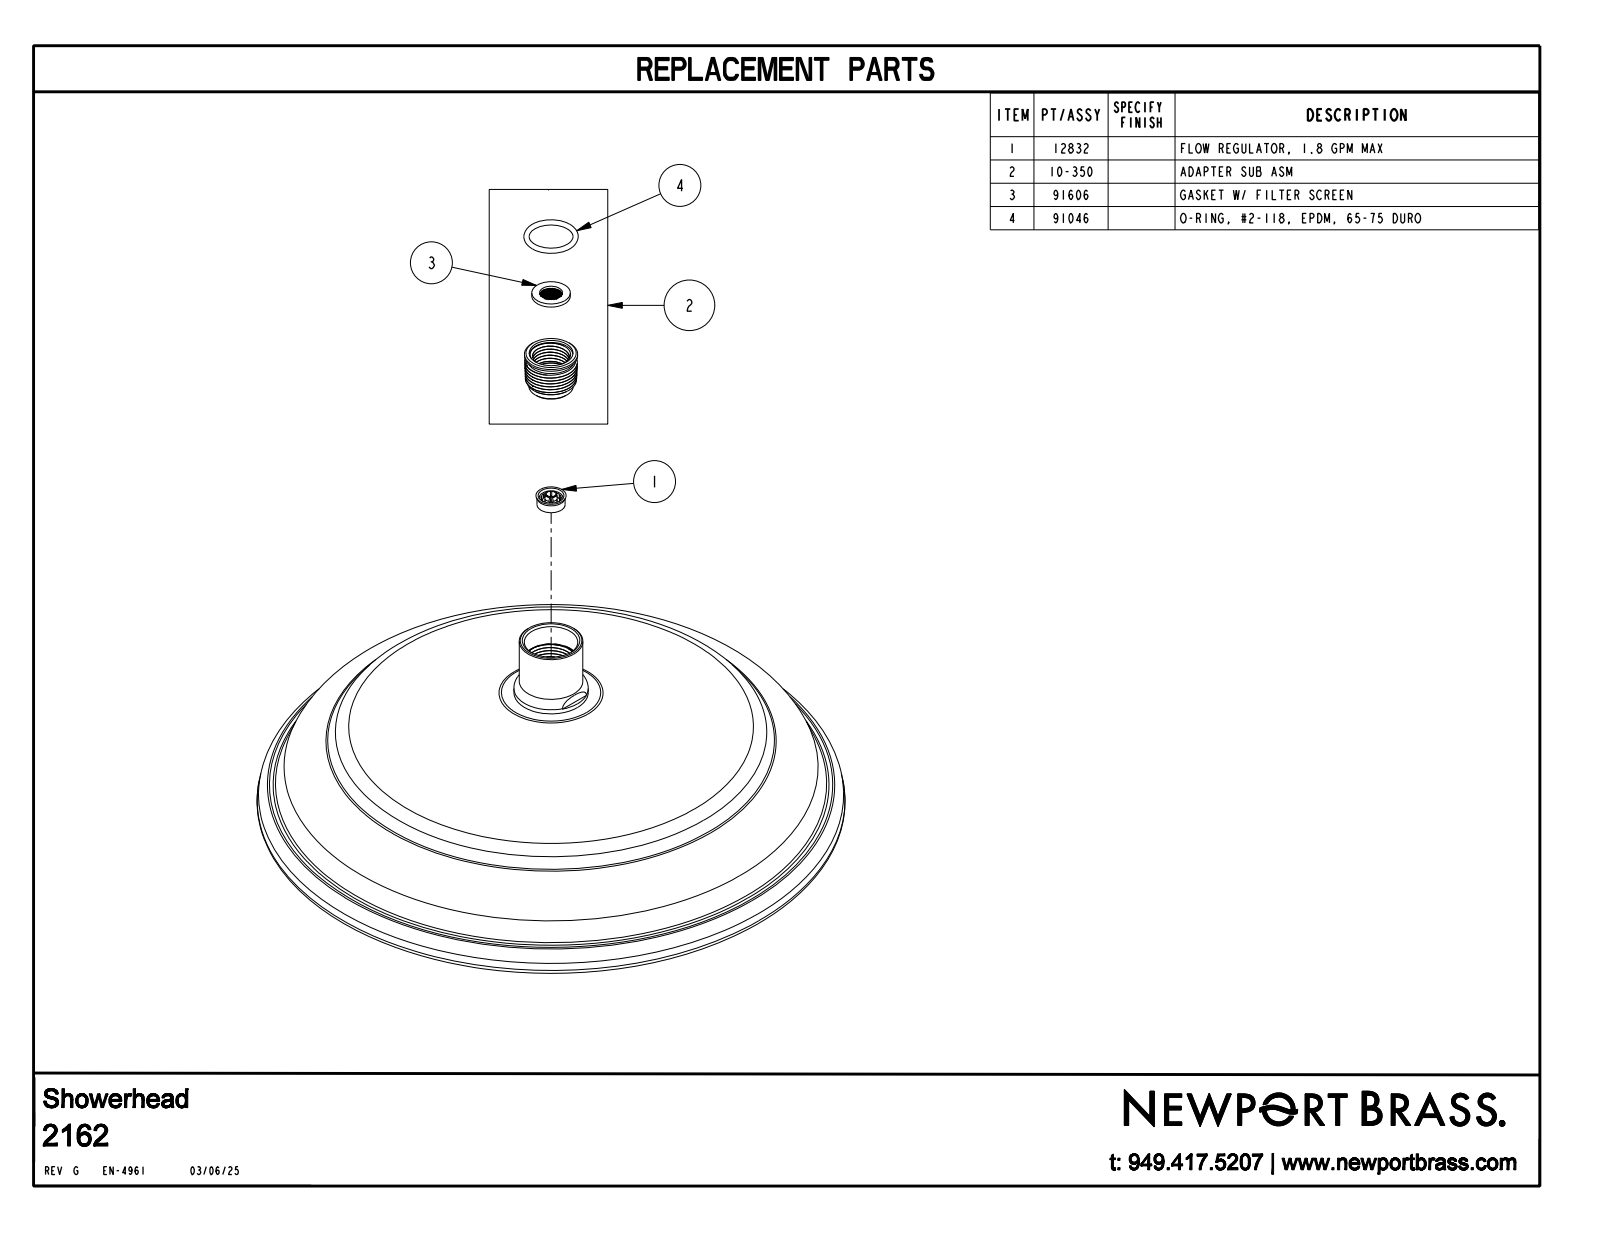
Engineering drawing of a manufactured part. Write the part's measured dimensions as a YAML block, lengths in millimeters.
part_name: "2162_SW00011"
step_written_by: "CREO PARAMETRIC BY PTC INC, 2023134 (CONFIG_CONTROL_DESIGN)"
units: millimeters
bodies: {solids: 1, faces: 2948, planar: 740, cylindrical: 1090, other: 1118}
overall_size: [293.4, 293.4, 99.4]
volume: 2825000
surface_area: 172900
round_holes:
  - {diameter: 2.2, count: 180}
  - {diameter: 4.1, count: 180}
  - {diameter: 13.8, count: 1}
  - {diameter: 280.7, count: 1}
round_bosses_or_shafts:
  - {diameter: 3.6, count: 180}
  - {diameter: 37.1, count: 1}
  - {diameter: 31.8, count: 1}
  - {diameter: 13.5, count: 1}
face_to_face_distances: [12.7, 12.7, 1.3, 69.1, 69.1, 56.4, 1.2, 11.5, 67.8, 1.3]
hole_center_spacings: [14.7, 14.7, 45.2, 22.8, 22.8, 32.4, 45.3, 16.7]
